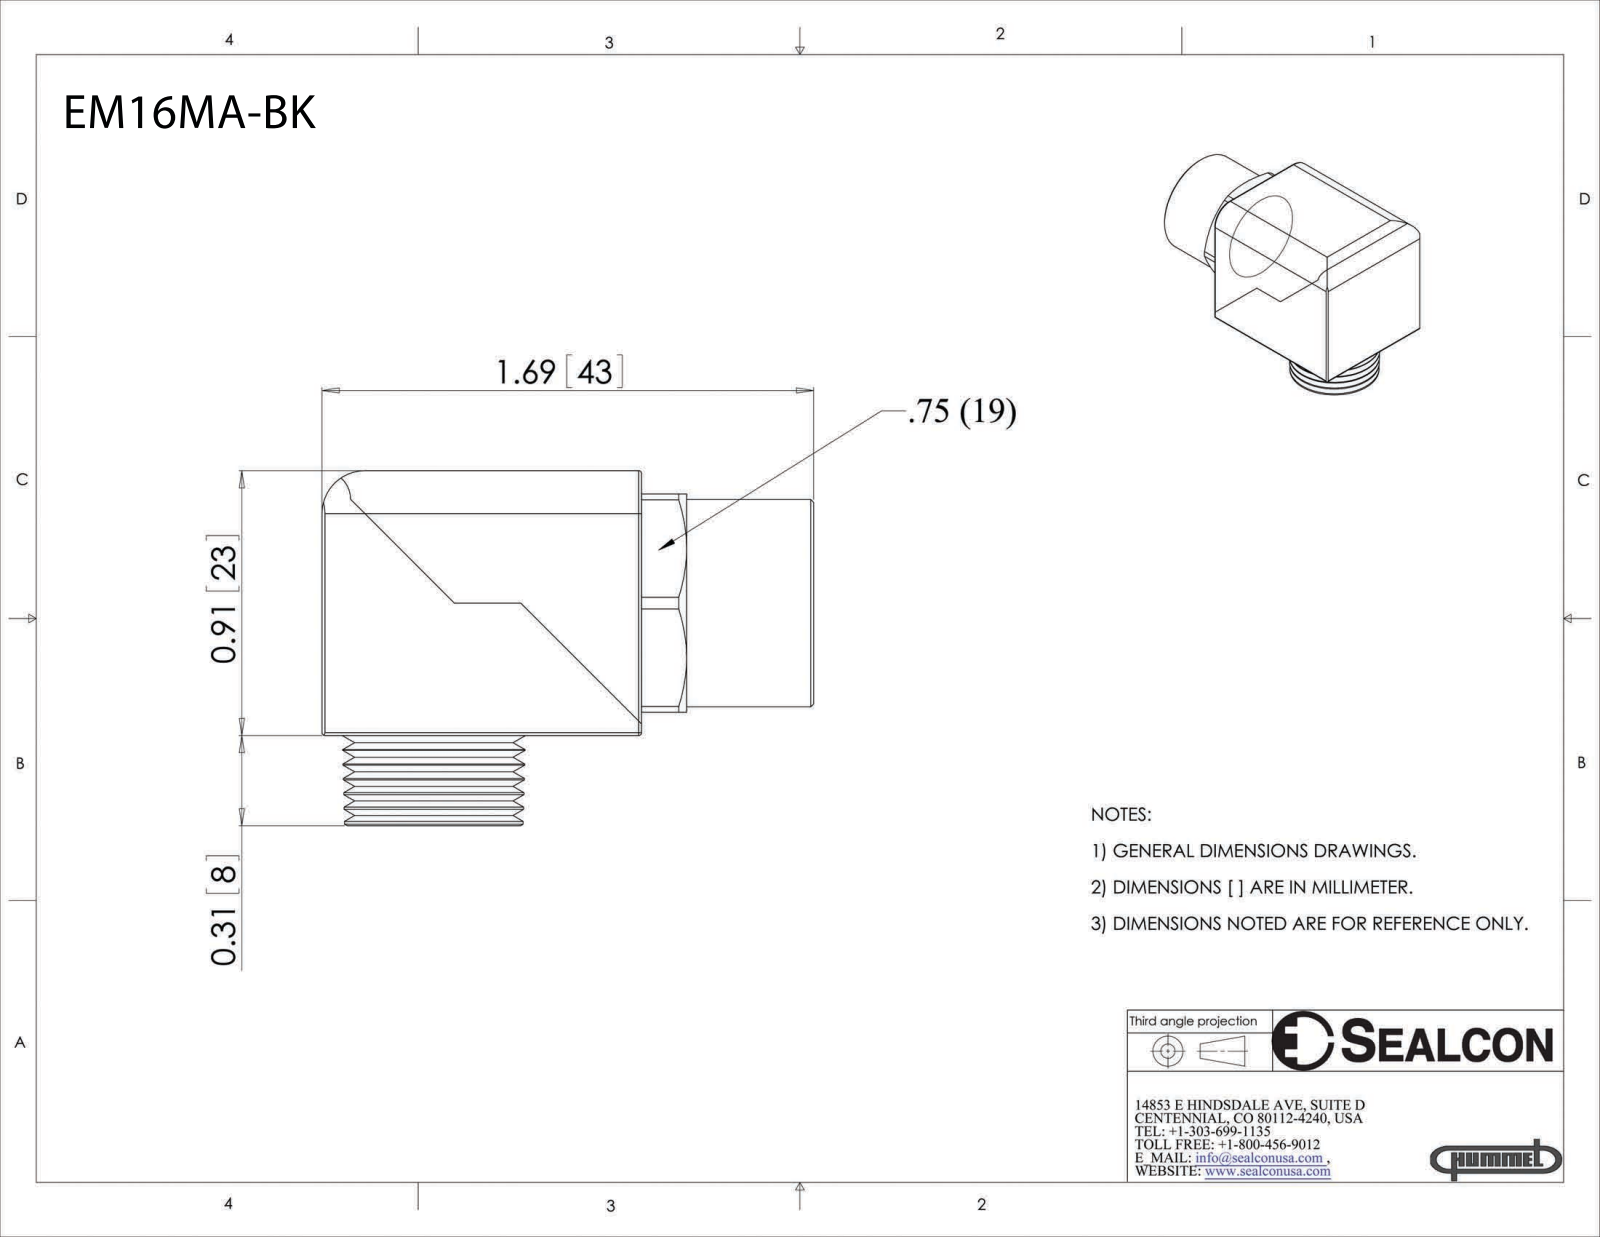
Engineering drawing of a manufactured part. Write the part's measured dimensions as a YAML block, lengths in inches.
part_name: "EM16MA-BK"
step_written_by: "SolidWorks 2007 (AUTOMOTIVE_DESIGN)"
units: inches
bodies: {solids: 2, faces: 122, planar: 31, cylindrical: 34, other: 57}
overall_size: [1.69, 1.22, 0.91]
volume: 0.992
surface_area: 12.52
round_holes:
  - {diameter: 0.347, count: 2}
  - {diameter: 0.48, count: 1}
round_bosses_or_shafts:
  - {diameter: 0.713, count: 1}
partial_cylinders:
  - {radius: 0.01, count: 7}
  - {radius: 0.147, count: 3}
  - {radius: 0.098, count: 1}
  - {radius: 0.422, count: 1}
face_to_face_distances: [0.91, 0.161, 1.098, 0.455, 0.592, 1.69, 0.31, 0.765, 1.22, 0.437]
